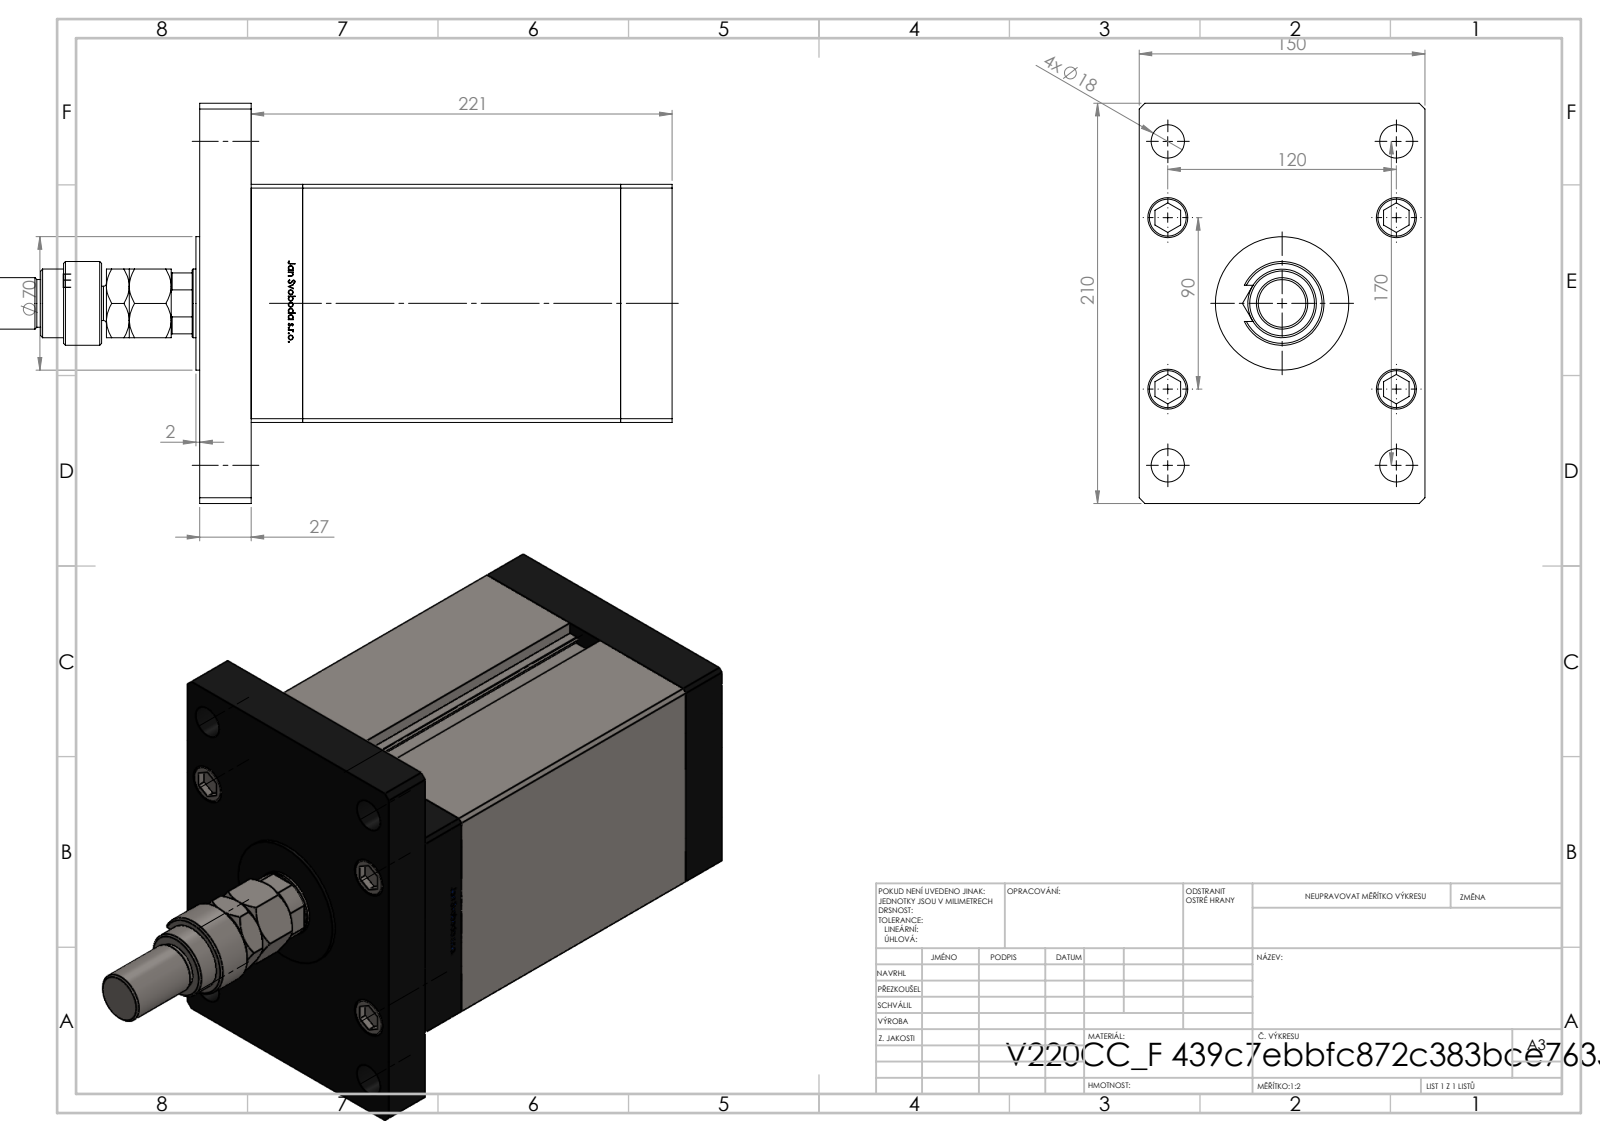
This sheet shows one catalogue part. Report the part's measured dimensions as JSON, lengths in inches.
{"part_name": "V220C BACK_F; V220C_F; MFA; FEMALE_PART_FOR_DFA (+4 more)", "step_written_by": "SolidWorks 2019 (CONFIG_CONTROL_DESIGN)", "units": "inches", "bodies": {"solids": 21, "faces": 1395, "planar": 545, "cylindrical": 200, "other": 650}, "overall_size": [14.705, 8.268, 5.906], "volume_in3": 272.3, "surface_area_in2": 764.5, "round_holes": [[0.689, 9], [0.866, 5], [0.63, 4], [0.827, 4], [0.079, 2], [0.518, 2], [1.004, 1], [1.417, 1], [1.476, 1]], "round_bosses_or_shafts": [[0.315, 9], [0.827, 5], [3.15, 1], [2.756, 1], [1.732, 1], [1.102, 1], [1.063, 1], [0.984, 1]], "partial_cylinders_radius": [[0.037, 2], [0.374, 1], [0.591, 1], [0.689, 1]], "face_to_face_distances": [1.063, 7.638, 8.701, 5.906, 4.921, 6.575, 2.126, 9.764, 1.319, 0.256], "hole_center_spacings": [2.008, 1.575, 2.953, 4.096, 4.724, 4.98, 5.118, 6.965]}
